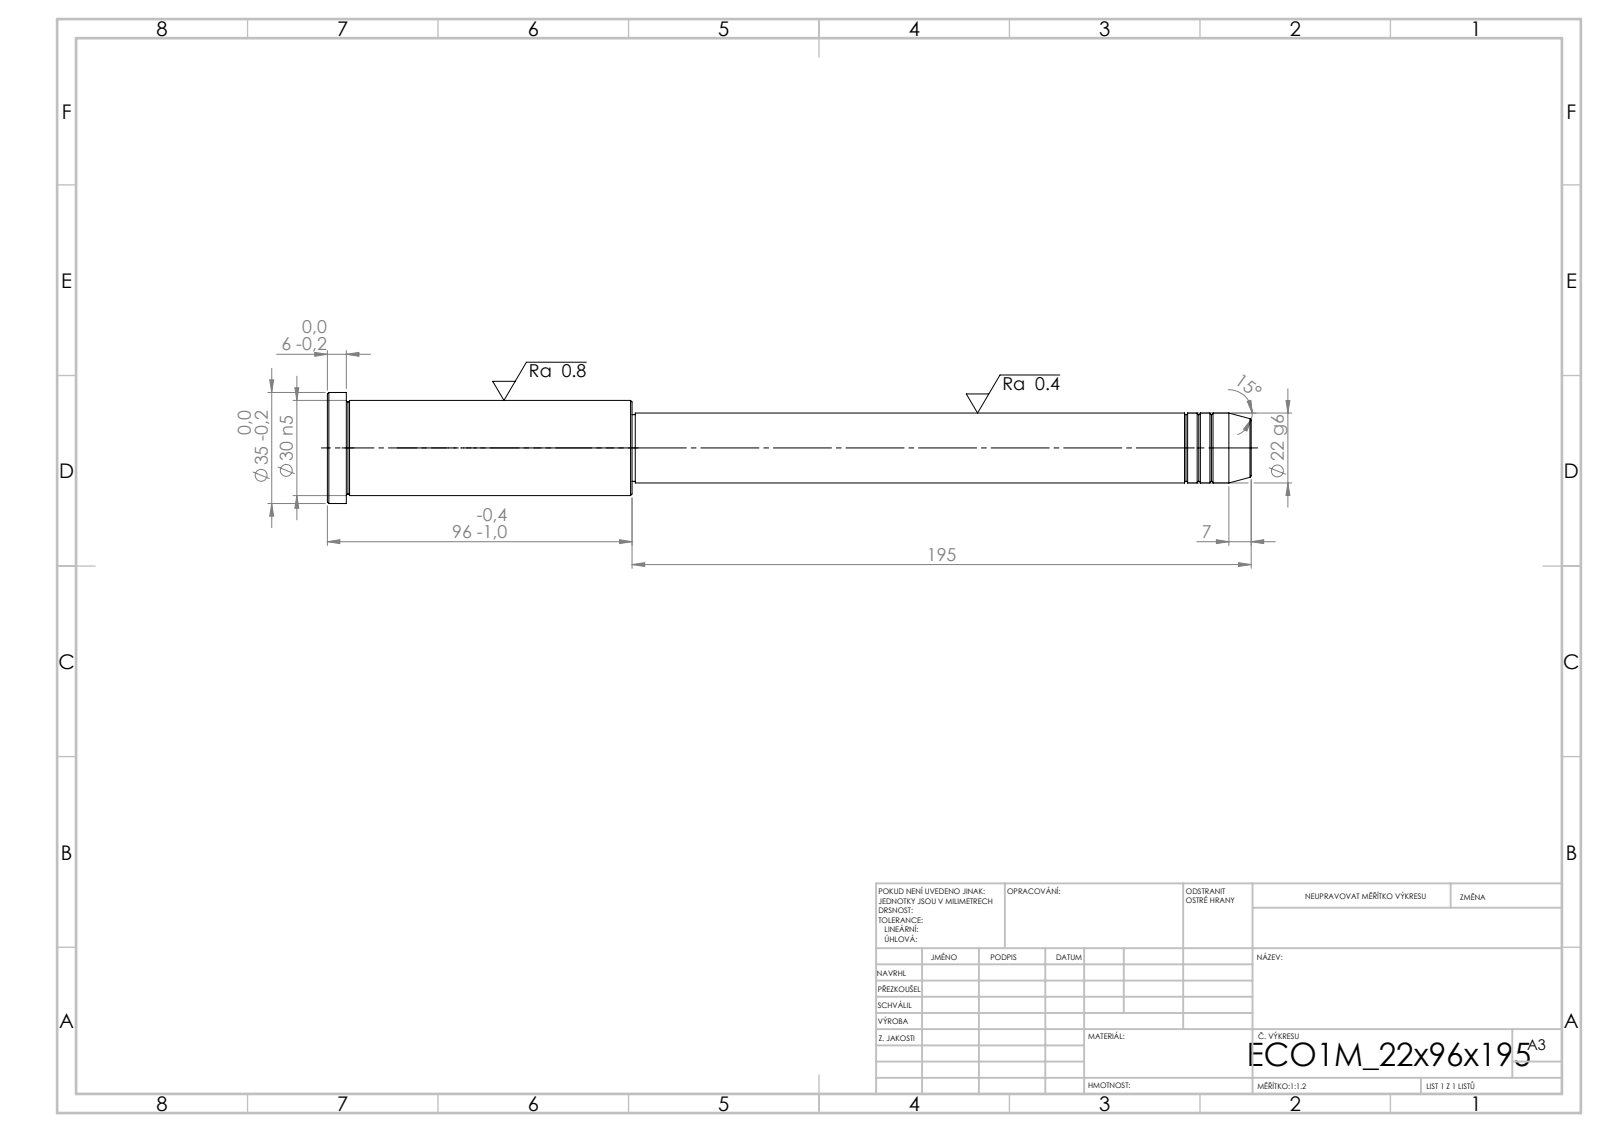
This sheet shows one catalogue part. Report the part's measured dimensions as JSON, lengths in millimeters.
{"step_written_by": "SolidWorks 2019 (CONFIG_CONTROL_DESIGN)", "units": "millimeters", "bodies": {"solids": 1, "faces": 43, "planar": 5, "cylindrical": 14, "other": 24}, "overall_size": [291, 35, 35], "volume_mm3": 142911, "surface_area_mm2": 24556, "round_bosses_or_shafts": [[35, 1], [30, 1], [22, 1], [21, 1]], "face_to_face_distances": [96, 90, 6, 195, 285, 291, 194, 1, 91, 97]}
